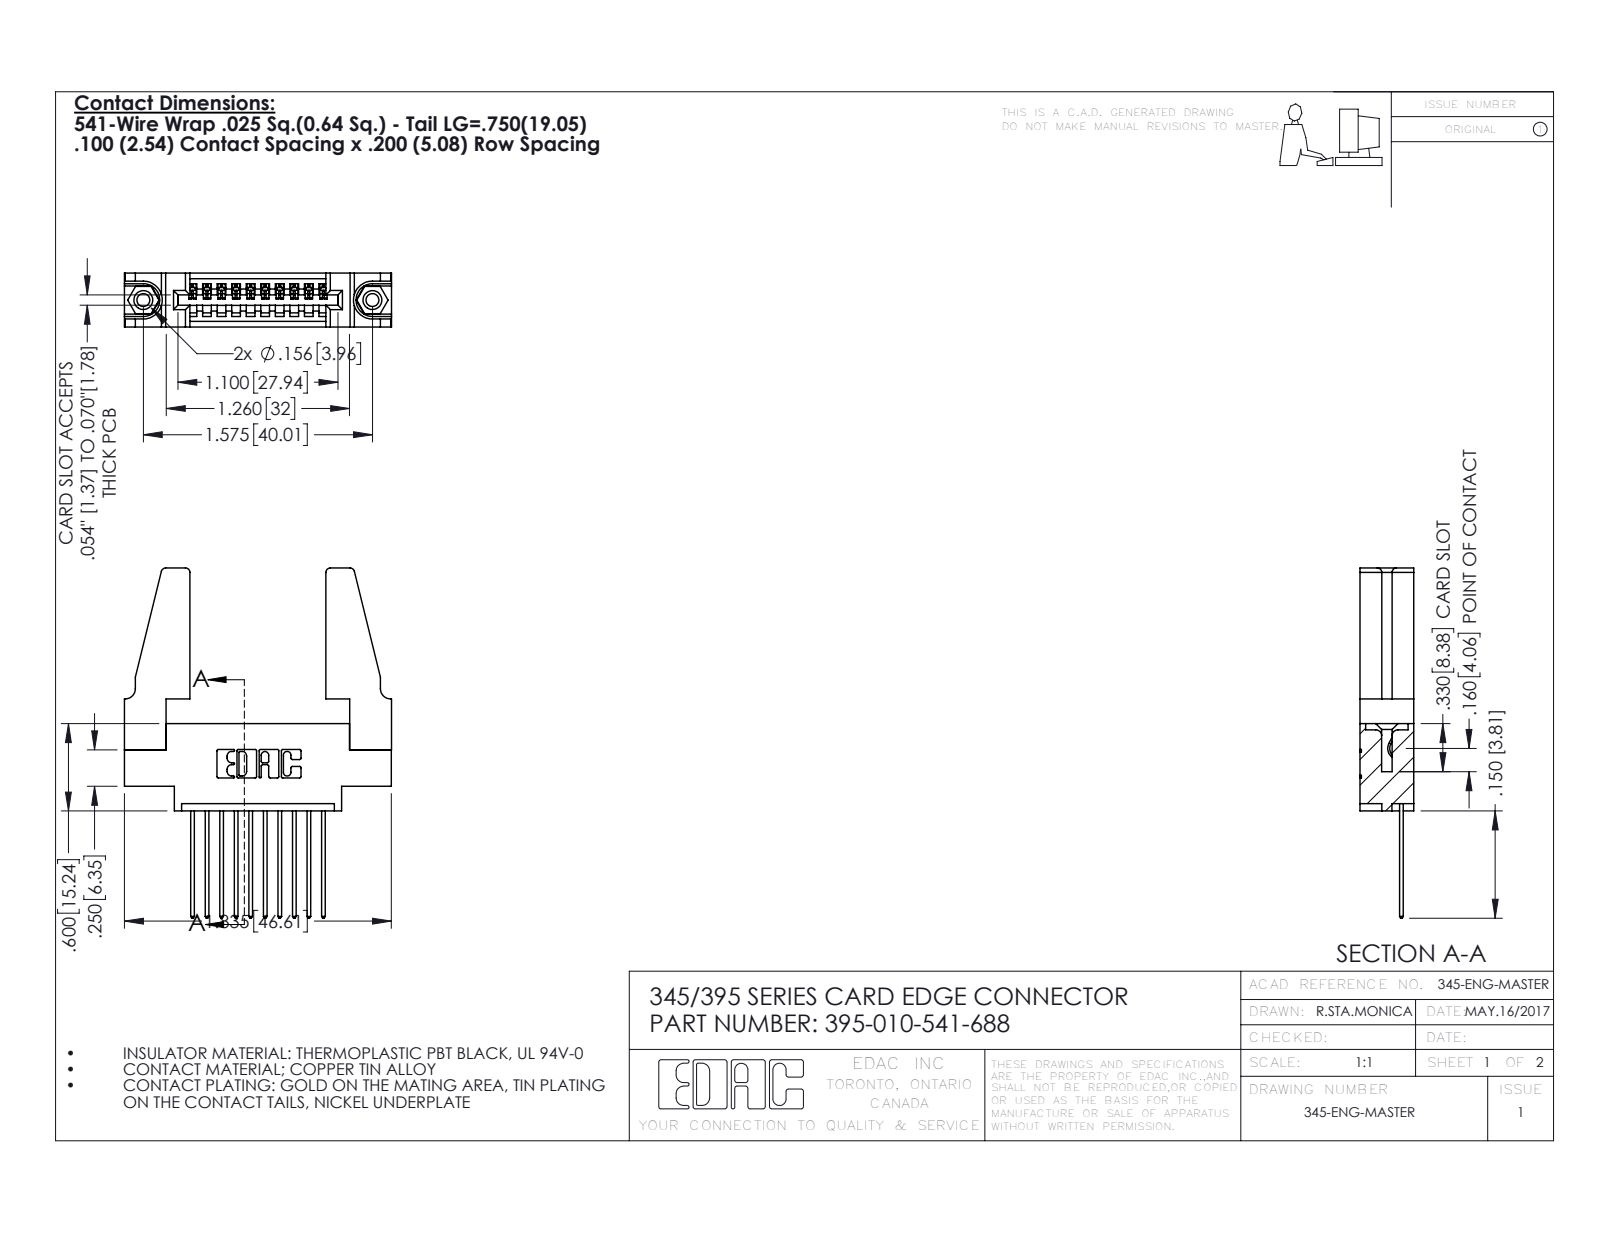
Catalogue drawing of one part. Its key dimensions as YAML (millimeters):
part_name: "395-010-541-688; 345-250-001_345-250-001-102; 345 Part_0.170 Offset - 0.156 Dia-TH; 345-220-078_345-220-088 (+1 more)"
step_written_by: "SolidWorks 2016 (CONFIG_CONTROL_DESIGN)"
units: millimeters
bodies: {solids: 15, faces: 834, planar: 556, cylindrical: 262, other: 16}
overall_size: [61.1, 46.6, 9.4]
volume: 7340
surface_area: 8445
round_holes:
  - {diameter: 2.3, count: 2}
  - {diameter: 3.2, count: 2}
  - {diameter: 4, count: 2}
  - {diameter: 1.6, count: 1}
round_bosses_or_shafts:
  - {diameter: 3.9, count: 2}
partial_cylinders:
  - {radius: 0.3, count: 22}
  - {radius: 0.2, count: 20}
  - {radius: 0.3, count: 20}
  - {radius: 0.8, count: 8}
  - {radius: 0.2, count: 6}
  - {radius: 0.8, count: 6}
  - {radius: 0.7, count: 3}
  - {radius: 0.8, count: 2}
face_to_face_distances: [9.4, 1.8, 7.6, 2.5, 6.9, 0.6, 5.1, 3.8, 3.8, 5.7]
hole_center_spacings: [6.9, 34.1, 40]
